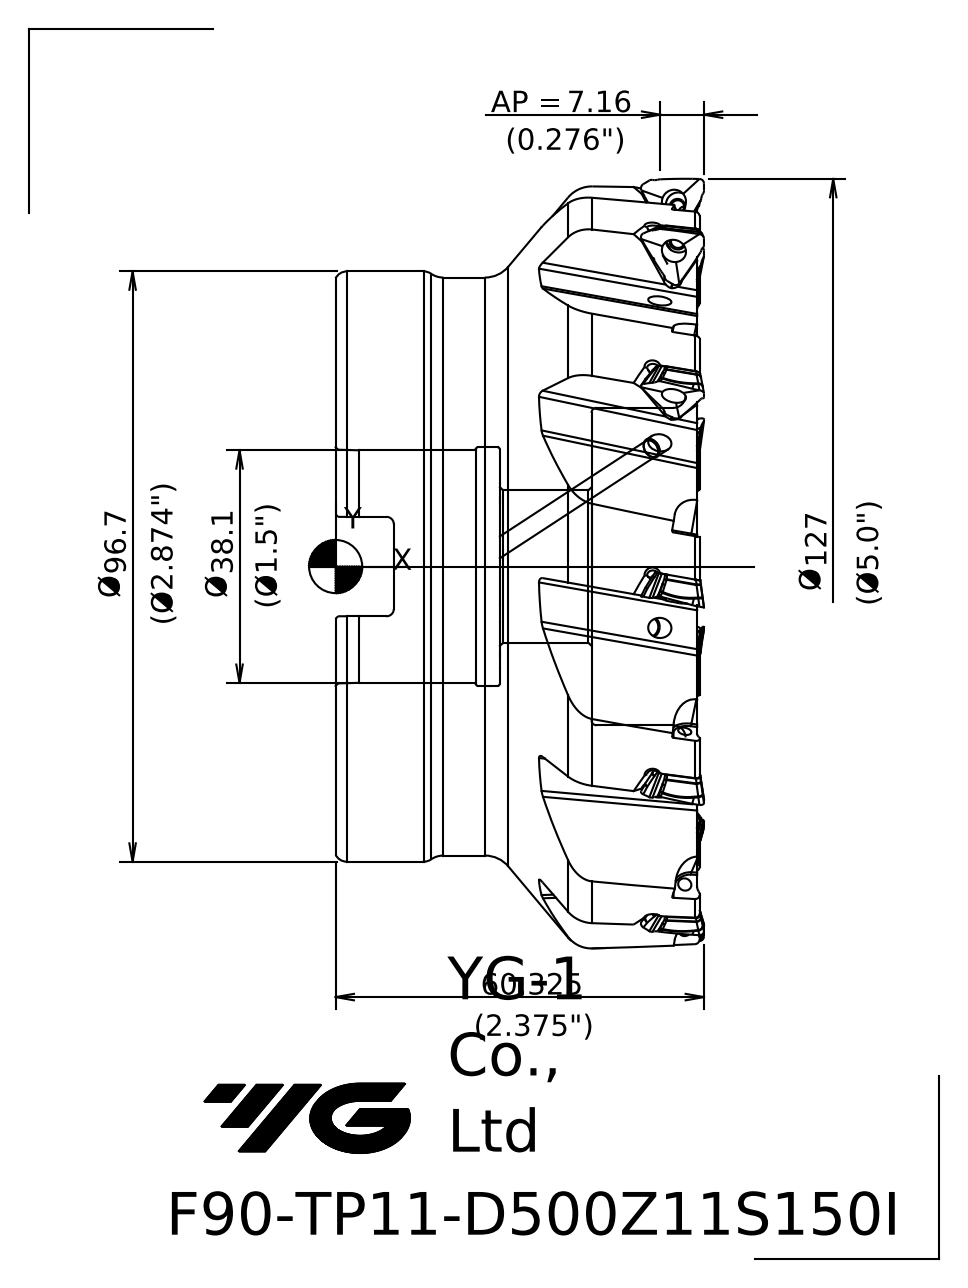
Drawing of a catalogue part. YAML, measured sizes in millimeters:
part_name: "10227DEC3C74p5rj"
step_written_by: "SIEMENS PLM Software NX 10.0 (AP203_CONFIGURATION_CONTROLLED_3D_DESIGN_OF_MECHANICAL_PARTS_AND_ASSEMBLIES_MIM_LF)"
units: millimeters
bodies: {solids: 1, faces: 76, planar: 18, cylindrical: 10, other: 48}
overall_size: [127.05, 127.05, 60.33]
volume: 464028
surface_area: 60005
round_holes:
  - {diameter: 25, count: 1}
  - {diameter: 38.1, count: 1}
  - {diameter: 39.1, count: 1}
  - {diameter: 52, count: 1}
round_bosses_or_shafts:
  - {diameter: 96.7, count: 1}
  - {diameter: 94.7, count: 1}
partial_cylinders:
  - {radius: 1.2, count: 2}
face_to_face_distances: [59.23, 1.9, 57.33, 17.3, 15.4, 41.93, 49.7, 47.8, 32.4, 9.53]
